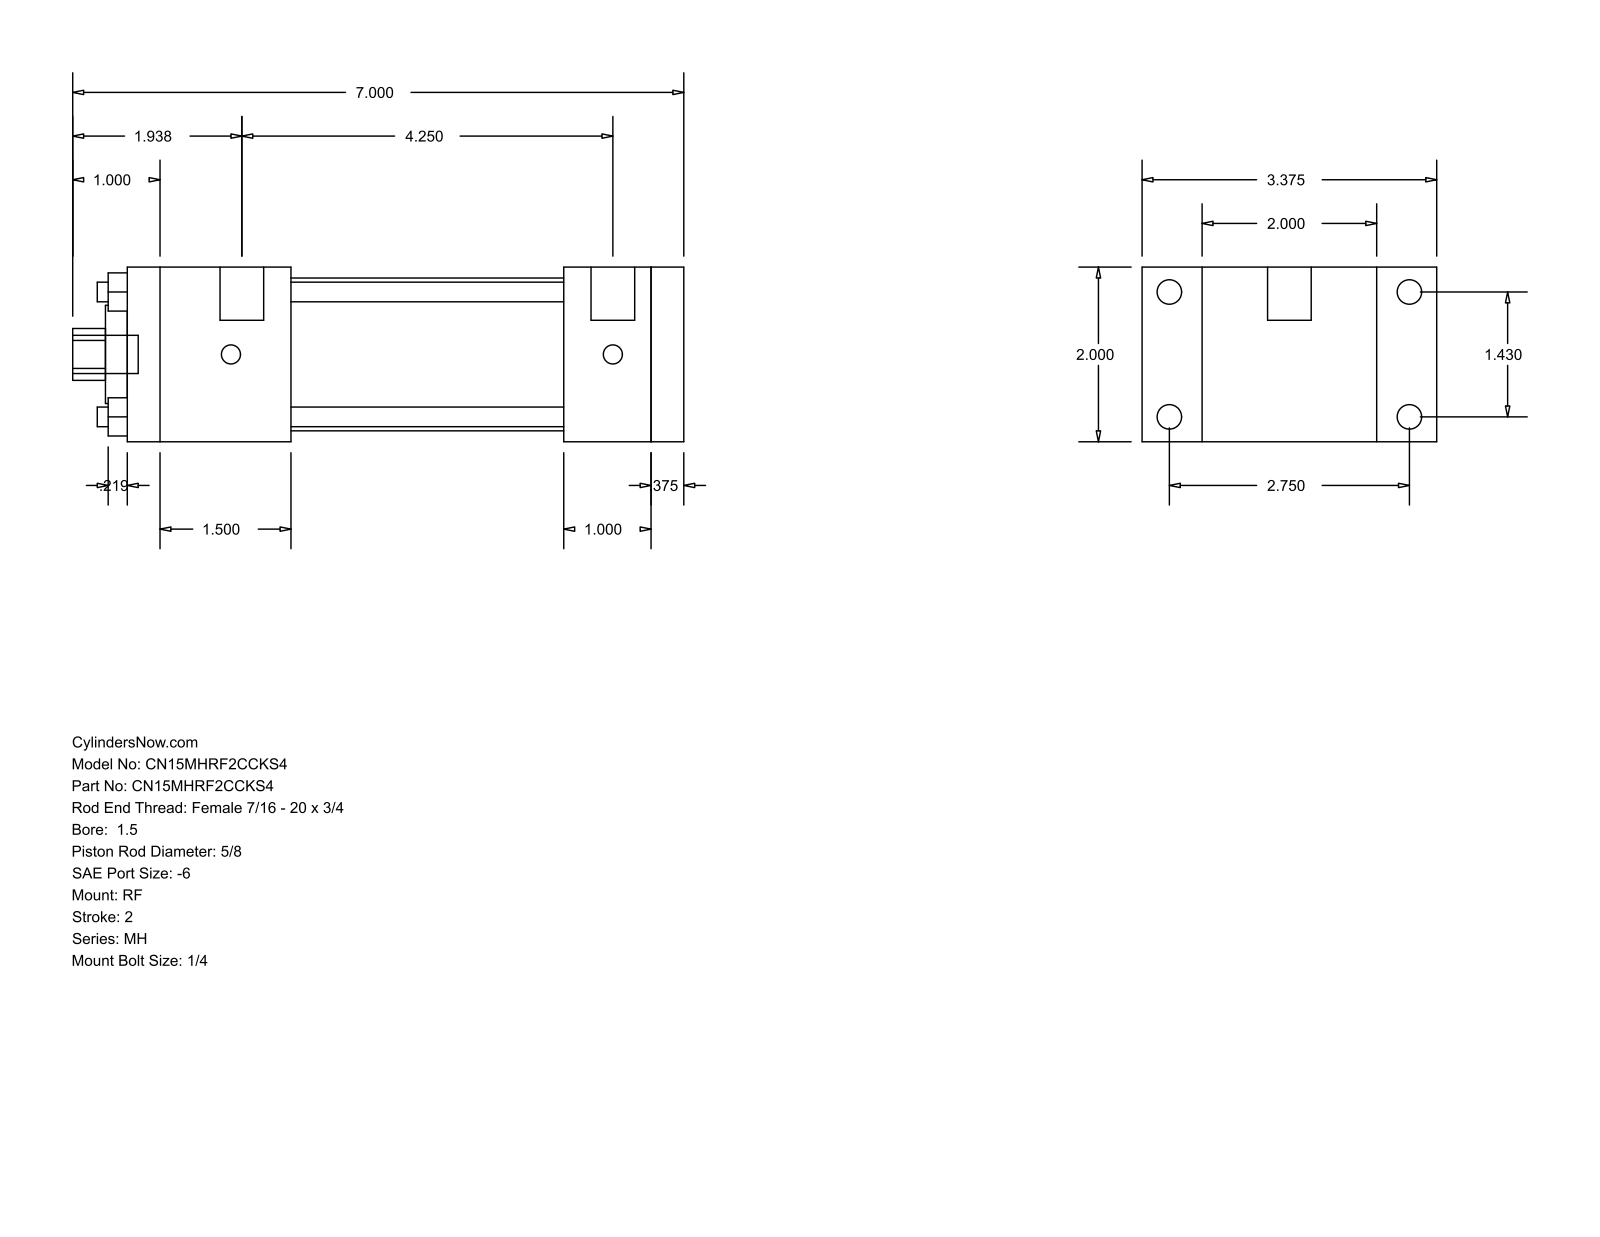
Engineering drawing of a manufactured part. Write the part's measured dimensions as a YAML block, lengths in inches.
part_name: "MH_RF__0150_0.625"
step_written_by: "GSSL Pune (CONFIG_CONTROL_DESIGN)"
units: inches
bodies: {solids: 0, faces: 92, planar: 64, cylindrical: 28, other: 0}
overall_size: [7, 3.375, 2]
round_holes:
  - {diameter: 0.225, count: 4}
  - {diameter: 0.625, count: 1}
  - {diameter: 1.125, count: 1}
  - {diameter: 1.75, count: 1}
round_bosses_or_shafts:
  - {diameter: 0.281, count: 4}
  - {diameter: 0.219, count: 4}
  - {diameter: 0.5, count: 2}
  - {diameter: 0.437, count: 1}
partial_cylinders:
  - {radius: 0.297, count: 1}
face_to_face_distances: [2, 0.375, 6, 6.375, 0.687, 2.687, 5, 1, 1.375, 1.875]
hole_center_spacings: [1.011, 1.43, 2.022]
